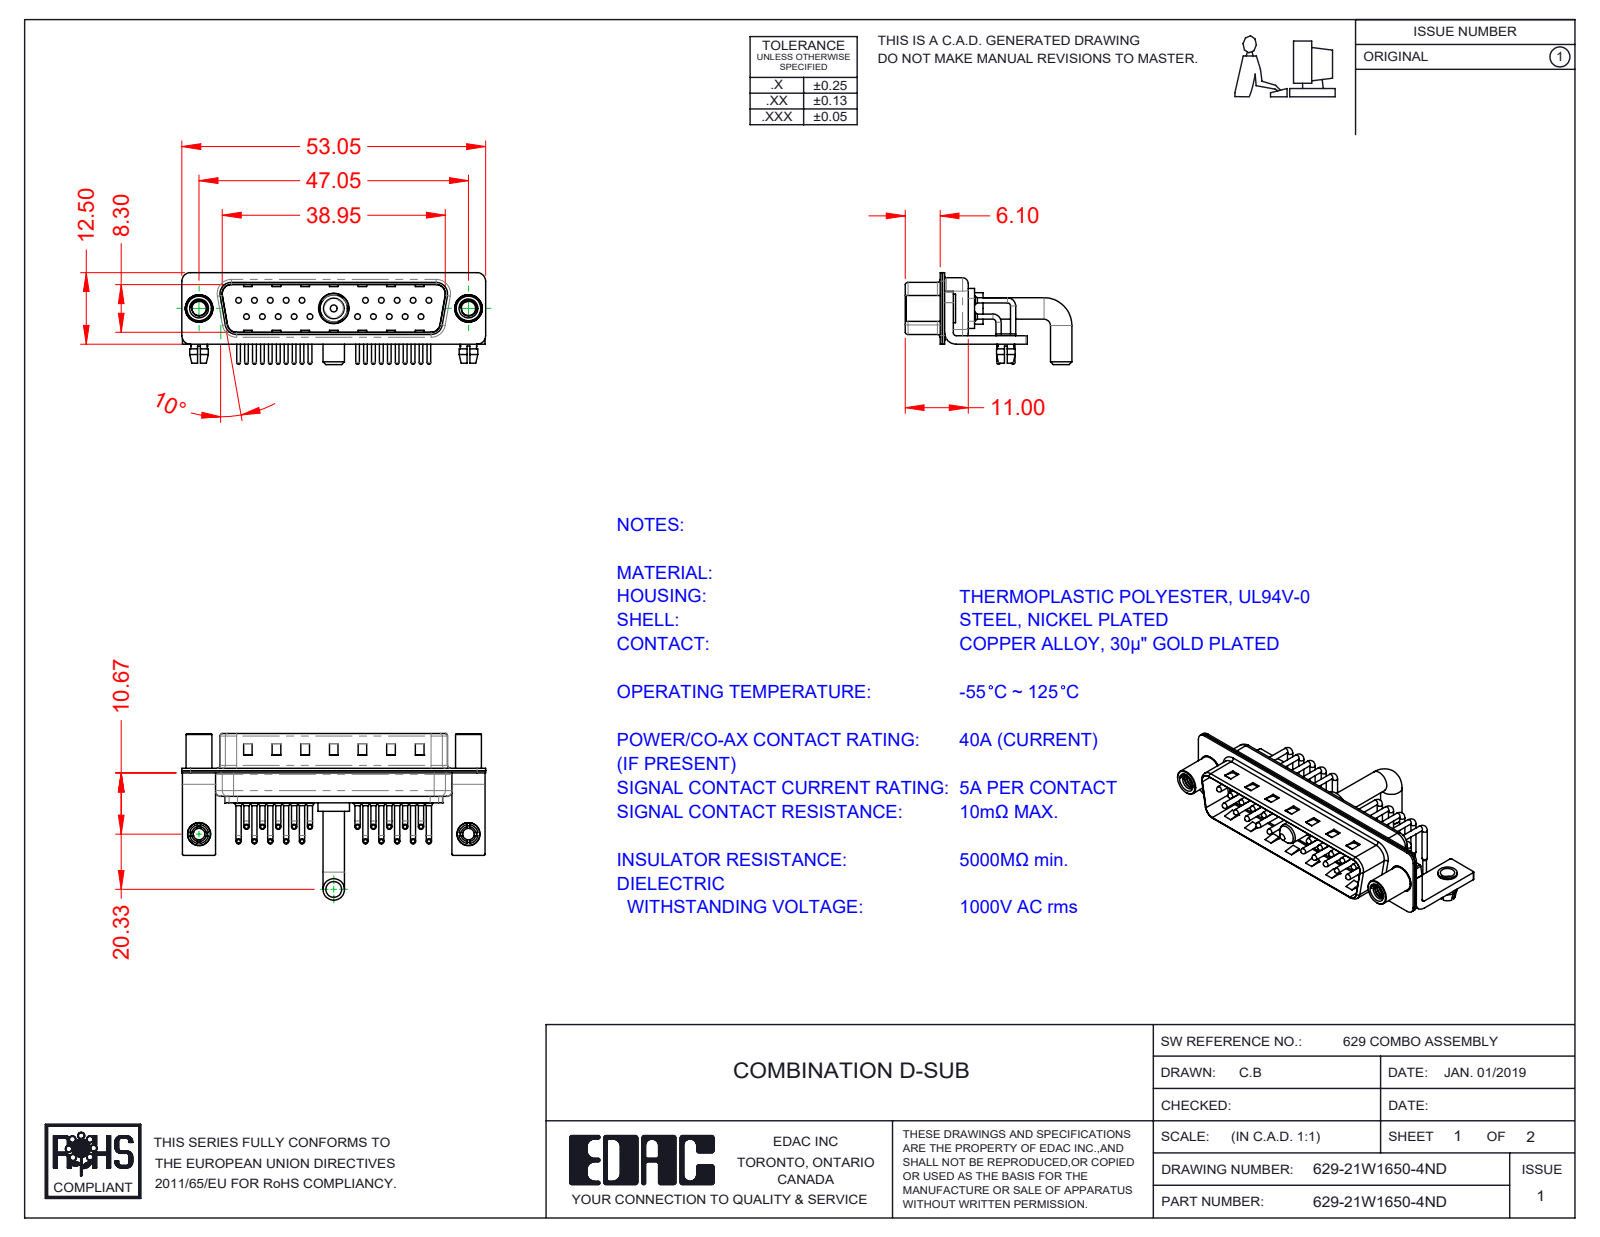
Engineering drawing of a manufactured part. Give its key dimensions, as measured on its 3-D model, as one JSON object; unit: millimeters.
{"part_name": "629Combo Contact Row 2; 629Combo Shell Front_25 Contacts; 629Combo Stabilizer Bracket; Power Pin_Ext 40A RA (+6 more)", "step_written_by": "SolidWorks 2020 (CONFIG_CONTROL_DESIGN)", "units": "millimeters", "bodies": {"solids": 31, "faces": 2809, "planar": 1531, "cylindrical": 982, "other": 296}, "overall_size": [53.05, 29.11, 16.05], "volume_mm3": 3589, "surface_area_mm2": 8858, "round_holes": [[2, 22], [0.75, 20], [1.6, 20], [2.5, 4], [3.2, 2], [4, 2], [4.8, 2], [4.85, 1], [5.3, 1]], "round_bosses_or_shafts": [[0.9, 40], [1.5, 20], [1, 20], [0.65, 20], [5, 2], [4.9, 2], [4.5, 2], [4, 2]], "partial_cylinders_radius": [[1.01, 20], [0.25, 16], [1.5, 16], [2, 13], [0.5, 9], [1.6, 8], [0.6, 4], [0.65, 4]], "face_to_face_distances": [0.4, 0.8, 9.5, 1.5, 9.1, 8.7, 9.9, 0.6, 2.1, 0.75], "hole_center_spacings": [3.16, 2.77, 5.54, 8.31, 5.04, 19.39, 20.97, 22.16]}
